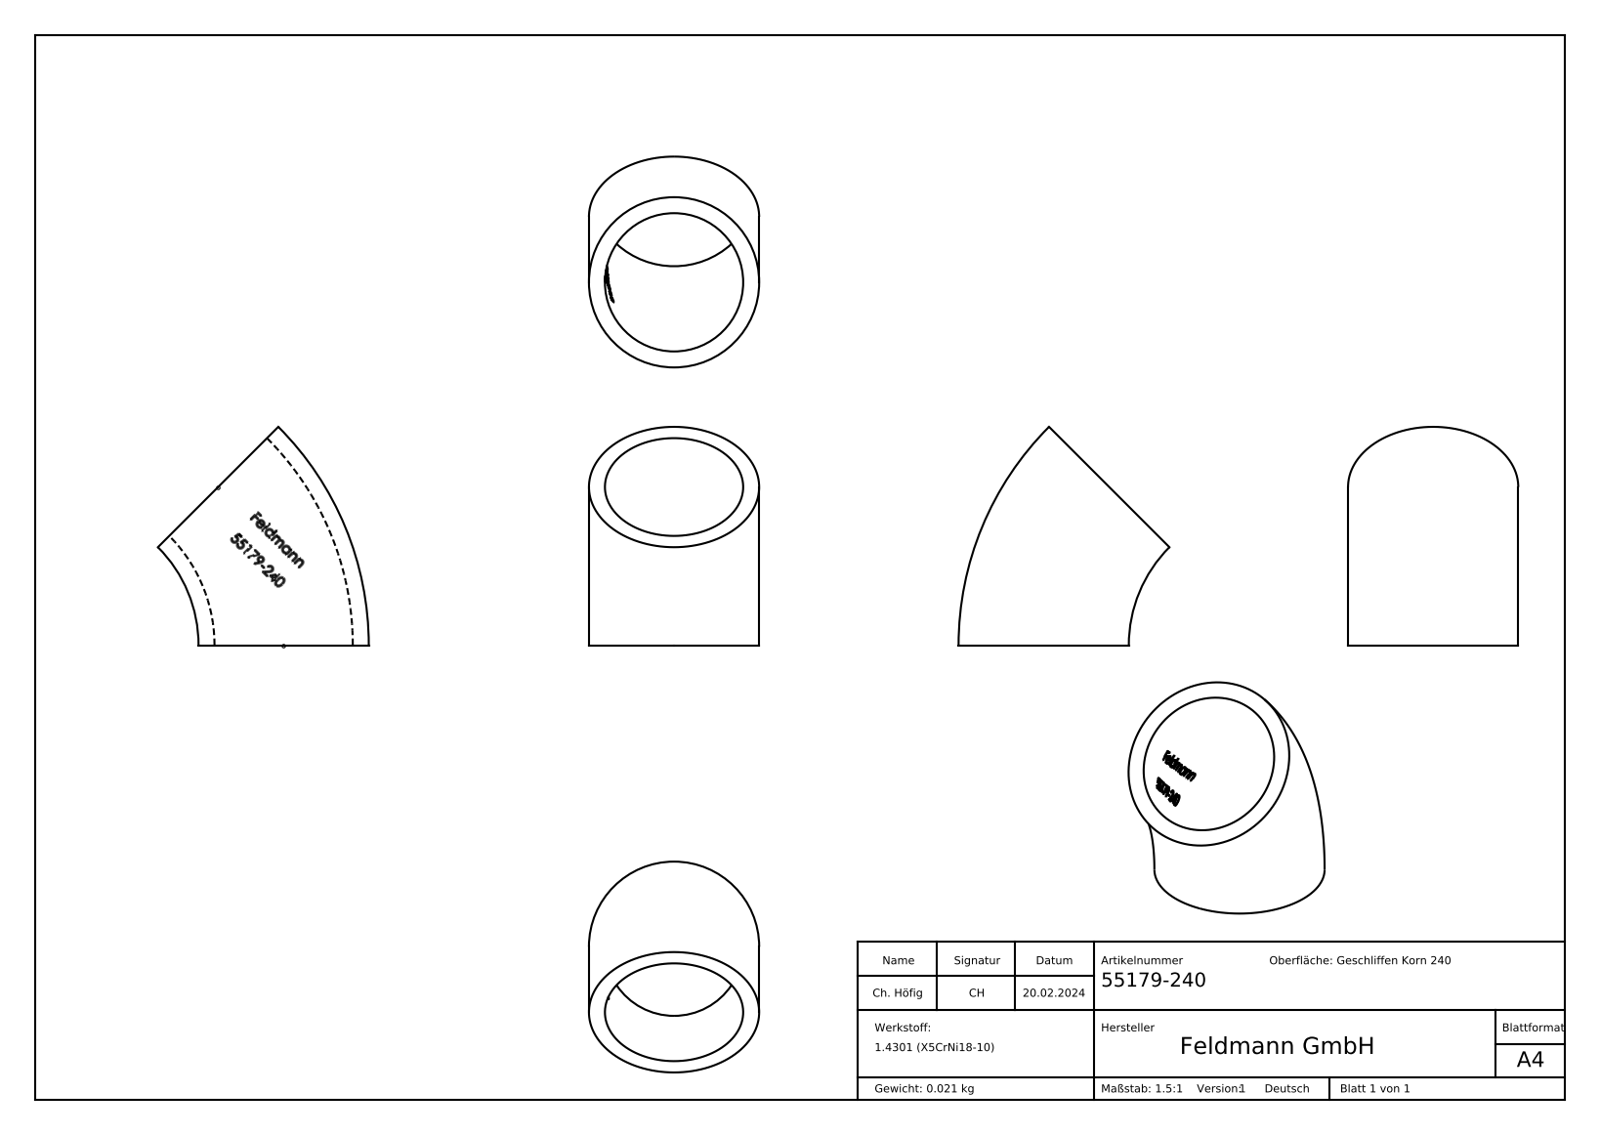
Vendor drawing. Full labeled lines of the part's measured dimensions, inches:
Part name (STEP PRODUCT): 55179-240
STEP written by: SolidWorks 2018 (CONFIG_CONTROL_DESIGN)
Units: inches
Bodies: 1 solid, 219 faces (106 planar, 0 cylindrical, 113 other)
Overall size (bounding box): 1.076 × 1.039 × 0.839
Volume: 0.163 in³ · Surface area: 4.524 in²
Main face-to-face distances: 0.193, 0.021, 0.048, 0.159, 0.133, 0.117, 0.033, 0.141, 0.095, 0.128
